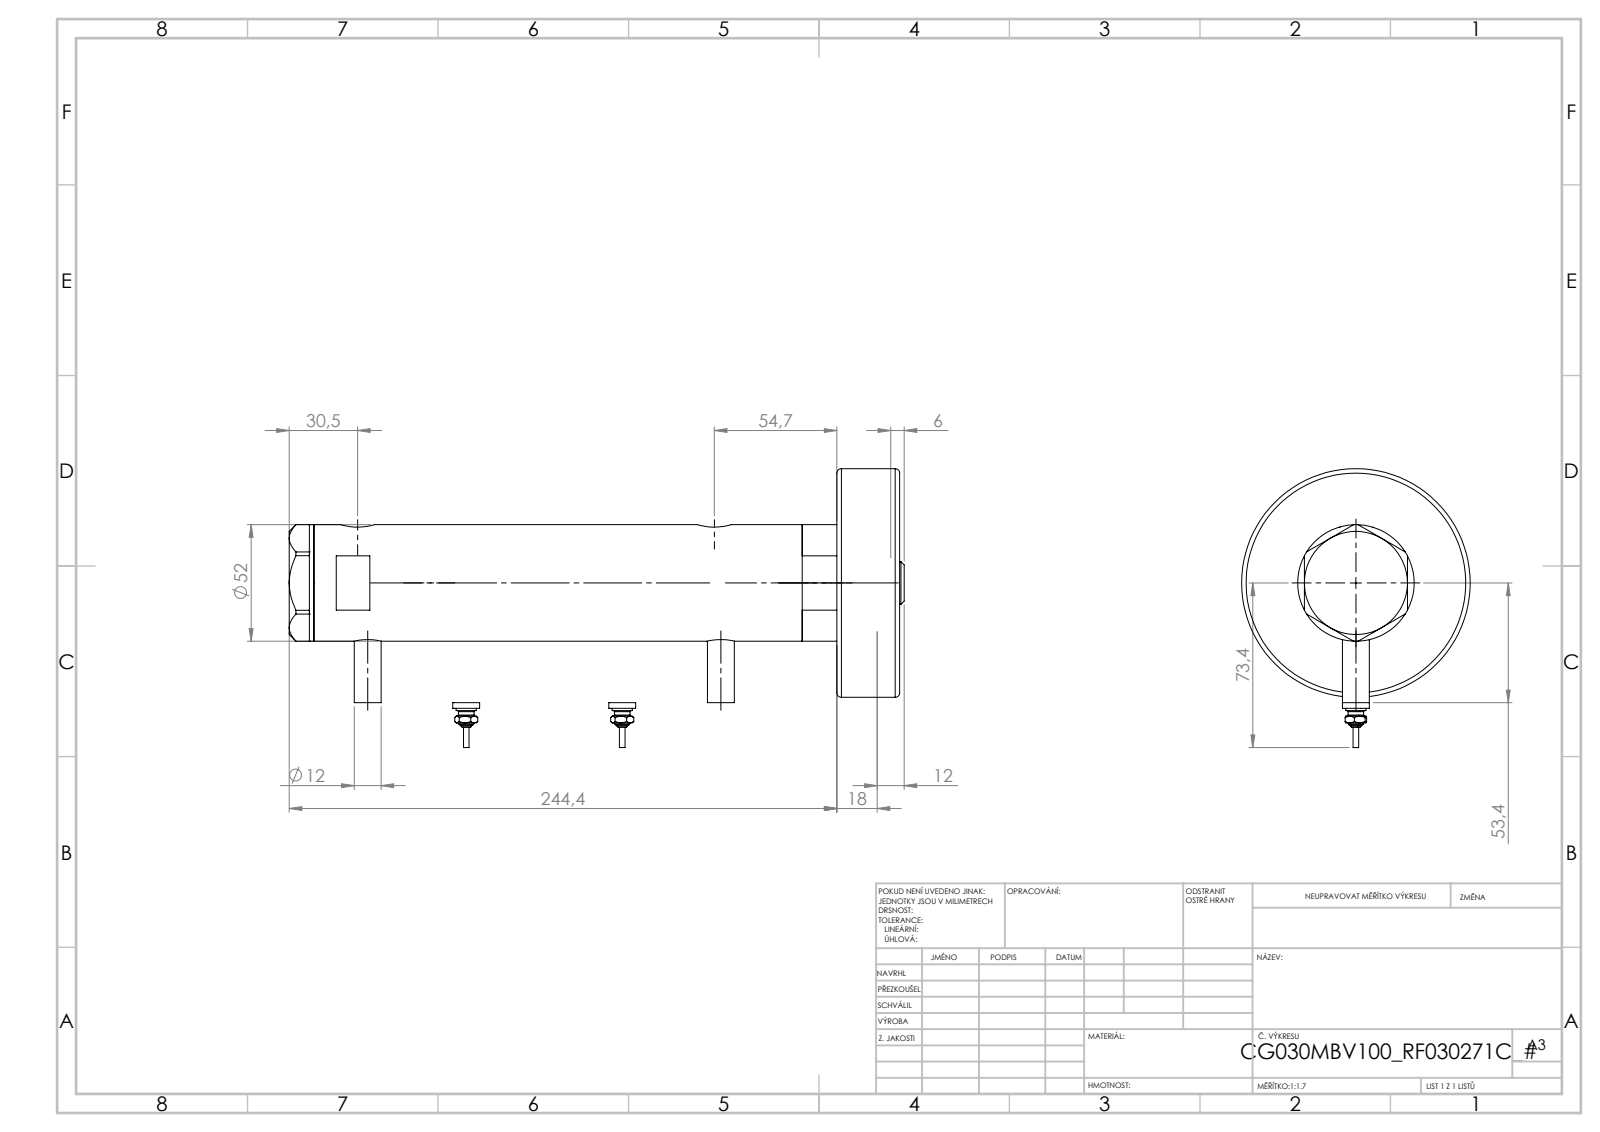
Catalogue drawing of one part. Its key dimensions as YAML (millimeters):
part_name: "V270CG_271C; V270CG_SWITCH; V270CG_VC; V270CG_MIDDLE (+2 more)"
step_written_by: "SolidWorks 2019 (CONFIG_CONTROL_DESIGN)"
units: millimeters
bodies: {solids: 7, faces: 256, planar: 97, cylindrical: 81, other: 78}
overall_size: [249.02, 109.3, 102]
volume: 636542
surface_area: 124847
round_holes:
  - {diameter: 5, count: 2}
  - {diameter: 9.73, count: 2}
  - {diameter: 12.5, count: 2}
  - {diameter: 15, count: 2}
  - {diameter: 6.5, count: 1}
  - {diameter: 20, count: 1}
  - {diameter: 21.5, count: 1}
  - {diameter: 30, count: 1}
  - {diameter: 33, count: 1}
  - {diameter: 40, count: 1}
  - {diameter: 44, count: 1}
round_bosses_or_shafts:
  - {diameter: 12, count: 3}
  - {diameter: 9, count: 2}
  - {diameter: 7, count: 2}
  - {diameter: 4.34, count: 2}
  - {diameter: 2.4, count: 2}
  - {diameter: 102, count: 1}
  - {diameter: 52, count: 1}
  - {diameter: 38, count: 1}
face_to_face_distances: [28, 205.44, 233.44, 51.9, 153.54, 79.9, 23.8, 129.74, 181.64, 209.64]
hole_center_spacings: [2.9, 4.5, 126.75, 129.65, 131.25, 134.15, 2.89, 2.91]
